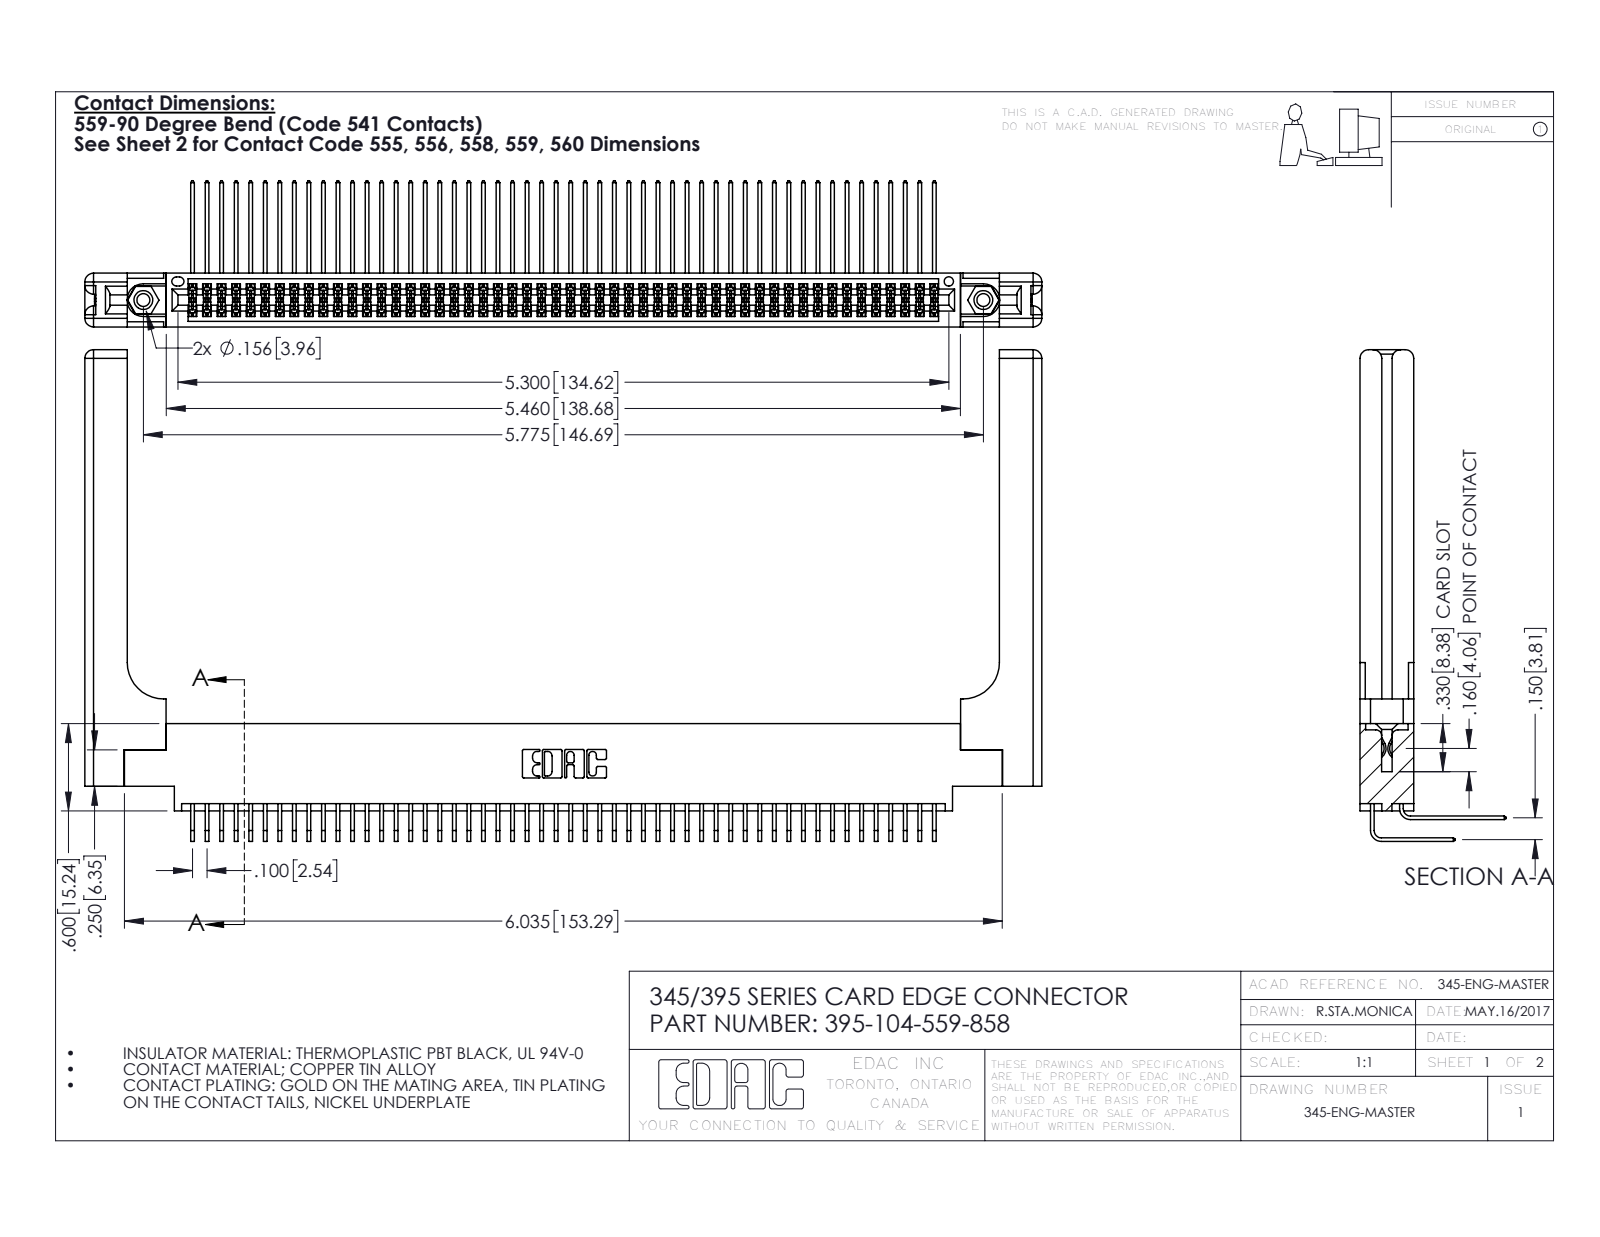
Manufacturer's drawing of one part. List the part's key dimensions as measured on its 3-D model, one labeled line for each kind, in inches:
Part name (STEP PRODUCT): 345 Part_0.170 Offset - 0.156 Dia-TH; 395-104-559-858; 345-292-001_558 559 Tail - 1; 345-250-001_345-250-001-102 (+2 more)
STEP written by: SolidWorks 2016 (CONFIG_CONTROL_DESIGN)
Units: inches
Bodies: 109 solids, 5794 faces (3872 planar, 1862 cylindrical, 60 other)
Overall size (bounding box): 6.579 × 3.379 × 1.005
Volume: 1.543 in³ · Surface area: 51.26 in²
Round holes (diameter × count): ⌀0.089 ×2, ⌀0.125 ×2, ⌀0.156 ×2, ⌀0.064 ×1
Round bosses / shafts (diameter × count): ⌀0.155 ×2
Partial cylindrical surfaces — rounded edges, fillets, slot ends (radius × count): R0.006 ×156, R0.01 ×22, R0.06 ×16, R0.007 ×6, R0.031 ×6, R0.026 ×3, R0.014 ×2, R0.019 ×2
Main face-to-face distances: 0.072, 0.298, 0.37, 0.098, 0.272, 0.025, 0.2, 0.225, 0.175, 0.15
Hole centre spacings: 0.27, 5.539, 5.775
